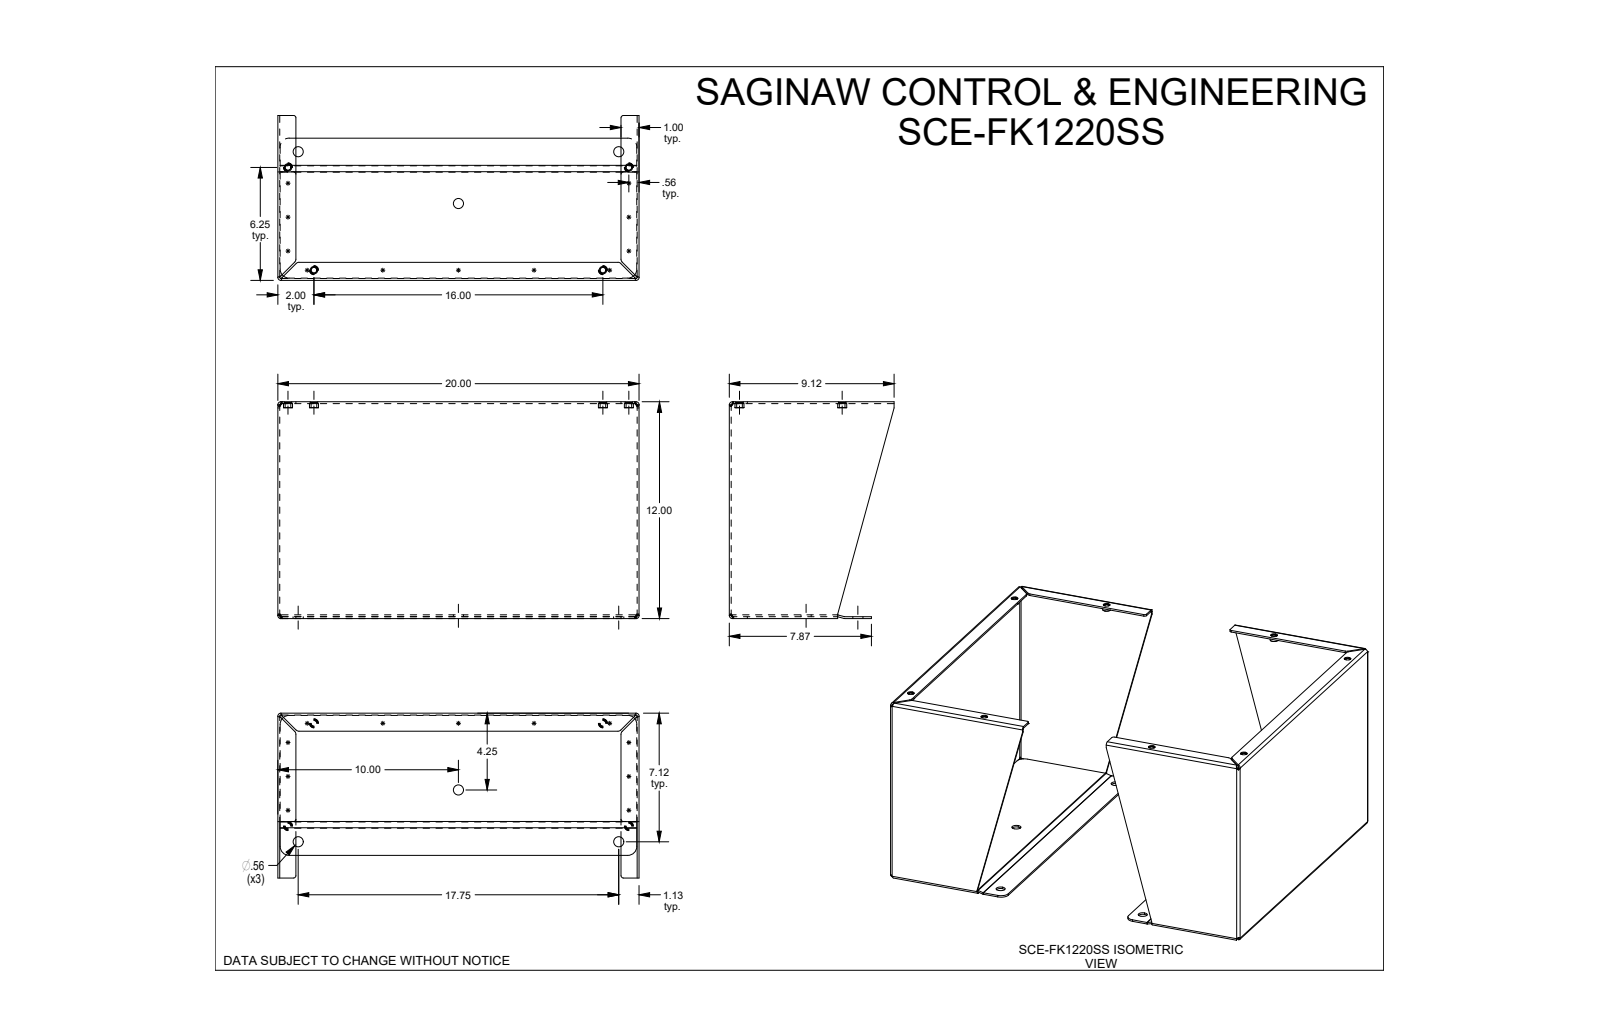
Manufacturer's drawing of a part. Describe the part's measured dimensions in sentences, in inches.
The part is named "SCE-FK1220SS". Its 3-D file was written by "SolidWorks 2019 (CONFIG_CONTROL_DESIGN)". It is 12 solids with 286 faces: 120 planar, 110 cylindrical and 56 other. Overall it measures 24 by 20 by 12 inches. Its volume is 130.2 cubic inches and its surface area 2 540 square inches. Round holes: 8 of diameter 0.312, 8 of diameter 0.413, 6 of diameter 0.563. Round bosses or shafts: 8 of diameter 0.5, 8 of diameter 0.412. Partial cylindrical surfaces (rounded edges, fillets, slot ends): 16 of radius 0.166, 10 of radius 0.062, 9 of radius 0.063, 8 of radius 0.125, 8 of radius 0.22, 8 of radius 0.5. The main face-to-face distances are 0.104, 23.896, 19.896, 24, 23.792, 20, 19.792, 11.792, 0.101, 11.893. The hole center spacings are 1.035, 5.866, 6.614, 8.809, 9.647, 10.646, 16.343, 16.47.
